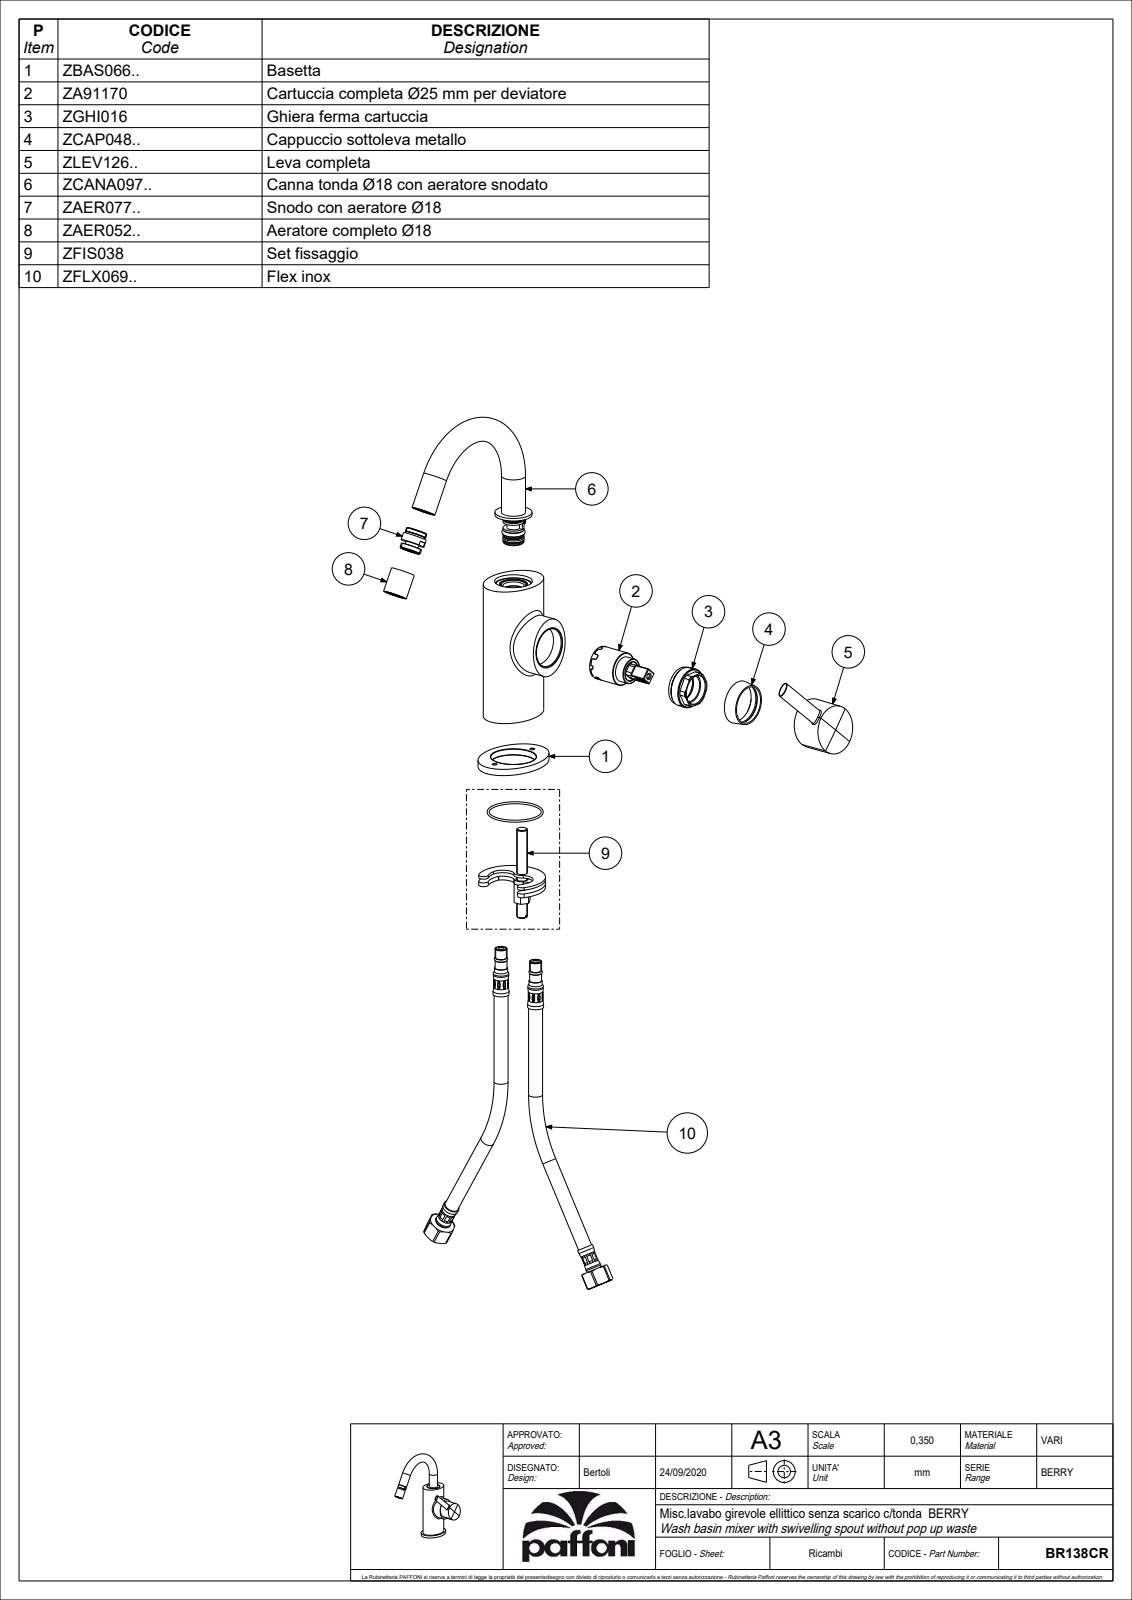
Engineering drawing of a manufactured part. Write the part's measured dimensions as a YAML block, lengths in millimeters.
part_name: "BR138CR"
step_written_by: "CREO PARAMETRIC BY PTC INC, 2020044 (CONFIG_CONTROL_DESIGN)"
units: millimeters
bodies: {solids: 2, faces: 1465, planar: 611, cylindrical: 555, other: 299}
overall_size: [197.09, 157.04, 83.2]
volume: 212880
surface_area: 79512
round_holes:
  - {diameter: 0.5, count: 51}
  - {diameter: 5, count: 4}
  - {diameter: 6, count: 4}
  - {diameter: 3, count: 2}
  - {diameter: 4, count: 2}
  - {diameter: 5.5, count: 2}
  - {diameter: 9.4, count: 2}
  - {diameter: 13, count: 2}
  - {diameter: 14, count: 2}
  - {diameter: 15, count: 2}
  - {diameter: 4.5, count: 1}
  - {diameter: 7, count: 1}
round_bosses_or_shafts:
  - {diameter: 10, count: 3}
  - {diameter: 9, count: 3}
  - {diameter: 18, count: 2}
  - {diameter: 38.8, count: 1}
  - {diameter: 28.5, count: 1}
  - {diameter: 27.8, count: 1}
  - {diameter: 25, count: 1}
  - {diameter: 20, count: 1}
partial_cylinders:
  - {radius: 0.5, count: 40}
  - {radius: 0.3, count: 17}
  - {radius: 1, count: 15}
  - {radius: 0.2, count: 13}
  - {radius: 0.15, count: 10}
  - {radius: 2, count: 10}
  - {radius: 1.25, count: 4}
  - {radius: 2.45, count: 4}
face_to_face_distances: [110, 3, 5, 2, 8, 7, 1.9, 0.5, 105, 102]
hole_center_spacings: [3.35, 1.5, 2.12, 4.74, 3, 5.41, 3.36, 6.71]
